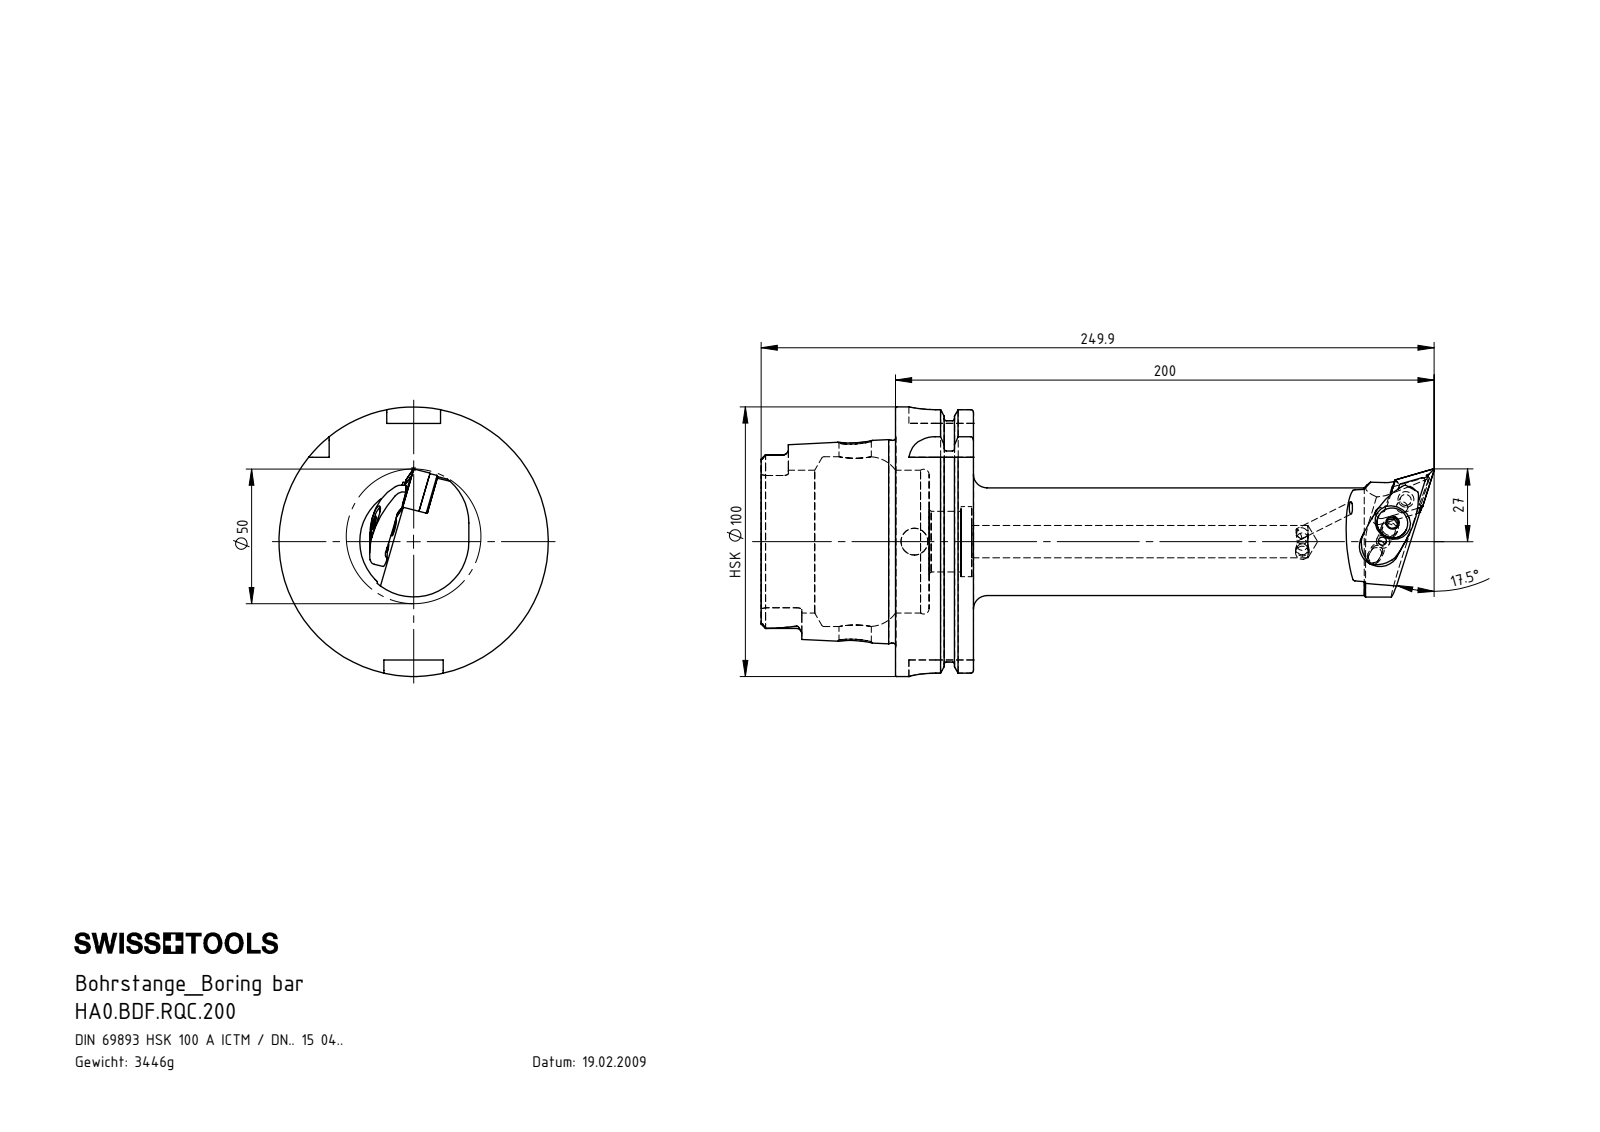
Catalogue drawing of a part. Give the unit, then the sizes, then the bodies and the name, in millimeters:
Units: millimetres
Overall size (bounding box): 249.9 × 100 × 100
Round holes (diameter × count): ⌀4.2 ×3, ⌀5 ×2, ⌀12 ×2, ⌀3 ×1, ⌀4 ×1, ⌀5.16 ×1, ⌀6.2 ×1, ⌀6.5 ×1, ⌀7 ×1, ⌀10 ×1, ⌀22.5 ×1, ⌀26 ×1
Round bosses / shafts (diameter × count): ⌀5 ×2, ⌀100 ×1, ⌀91.95 ×1, ⌀75.26 ×1, ⌀40 ×1, ⌀11.5 ×1, ⌀7 ×1, ⌀6.2 ×1
Partial cylindrical surfaces — rounded edges, fillets, slot ends (radius × count): R0.39 ×6, R0.69 ×6, R1.9 ×6, R0.4 ×4, R10 ×4, R0.8 ×2, R2 ×2, R3 ×2
Main face-to-face distances: 28.95, 12.45, 16.5, 49.9, 62.35, 78.85, 87.8, 78.2, 28.3, 15.85
Hole centre spacings: 8, 8.2, 14.8, 15.01, 23
Volume: 439 946 mm³ · Surface area: 79 665 mm²
Bodies: 9 solids, 409 faces (104 planar, 134 cylindrical, 171 other)
Part name (STEP PRODUCT): WCC-ER2.001.010_A; WCC-ER3.102.024_C; WDF-ER2.101.003_A; HA0.BDF.RQC.200 (+5 more)
STEP written by: SolidWorks 2017 (AUTOMOTIVE_DESIGN)
